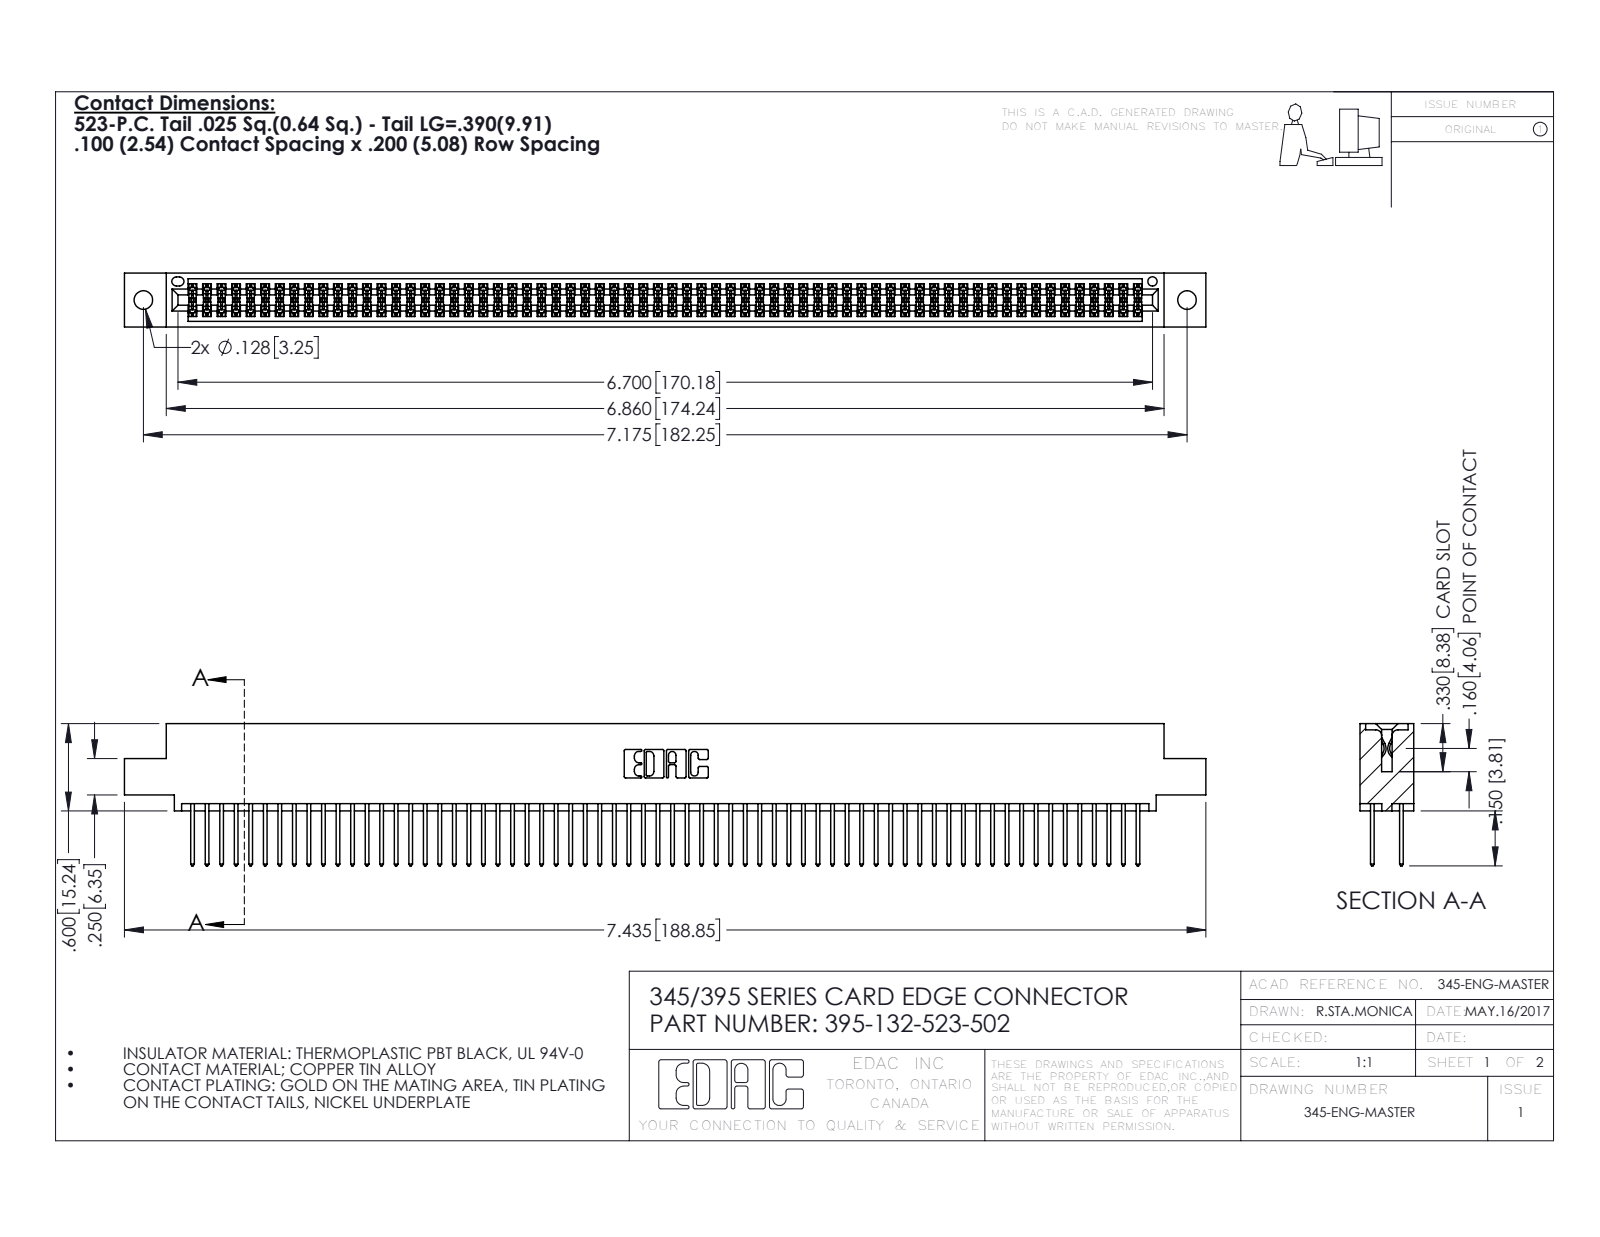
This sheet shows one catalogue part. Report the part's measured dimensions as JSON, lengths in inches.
{"part_name": "395-132-523-502; 345 Part_0.110 Offset - 0.128 Dia; 345-292-001_345-293-123", "step_written_by": "SolidWorks 2016 (CONFIG_CONTROL_DESIGN)", "units": "inches", "bodies": {"solids": 133, "faces": 6730, "planar": 4440, "cylindrical": 2290, "other": 0}, "overall_size": [7.435, 0.977, 0.37], "volume_in3": 1.143, "surface_area_in2": 45.23, "round_holes": [[0.128, 2], [0.064, 1]], "partial_cylinders_radius": [[0.006, 198], [0.01, 132], [0.01, 22], [0.007, 6], [0.031, 6], [0.026, 3], [0.014, 2], [0.019, 2]], "face_to_face_distances": [0.298, 0.072, 0.2, 0.098, 0.272, 0.025, 0.37, 0.225, 0.175, 0.149], "hole_center_spacings": [0.27, 6.939, 7.175]}
